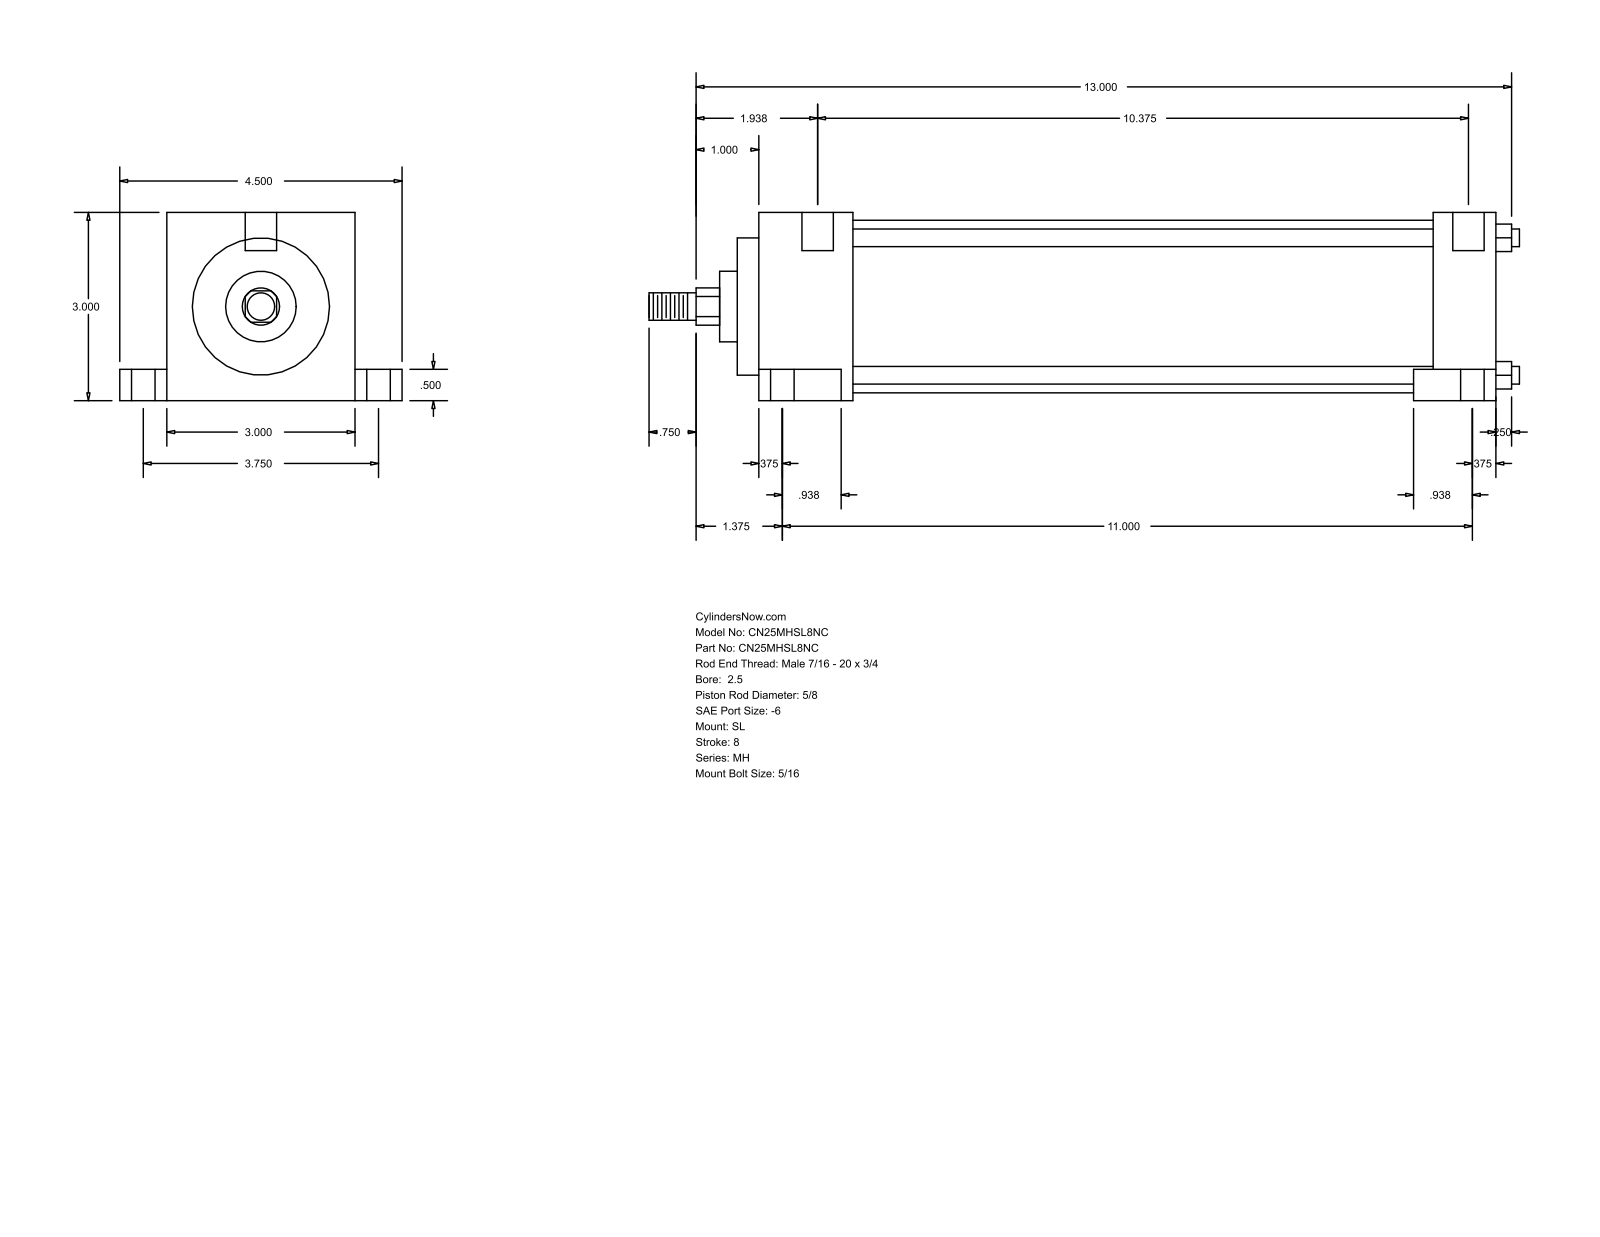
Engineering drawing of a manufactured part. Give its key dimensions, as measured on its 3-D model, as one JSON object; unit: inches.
{"part_name": "MH_SL__0250_0.625", "step_written_by": "GSSL Pune (CONFIG_CONTROL_DESIGN)", "units": "inches", "bodies": {"solids": 0, "faces": 86, "planar": 61, "cylindrical": 25, "other": 0}, "overall_size": [13.875, 4.5, 3], "round_holes": [[0.219, 2], [0.375, 2], [0.625, 2], [0.5, 1]], "round_bosses_or_shafts": [[0.281, 4], [2.75, 1], [2.187, 1], [1.125, 1], [0.625, 1], [0.437, 1]], "partial_cylinders_radius": [[0.297, 1]], "face_to_face_distances": [3, 1, 11.094, 12.094, 2.5, 0.5, 0.75, 3.75, 1.25, 10.781], "hole_center_spacings": [1.876, 0.125, 3.75]}
